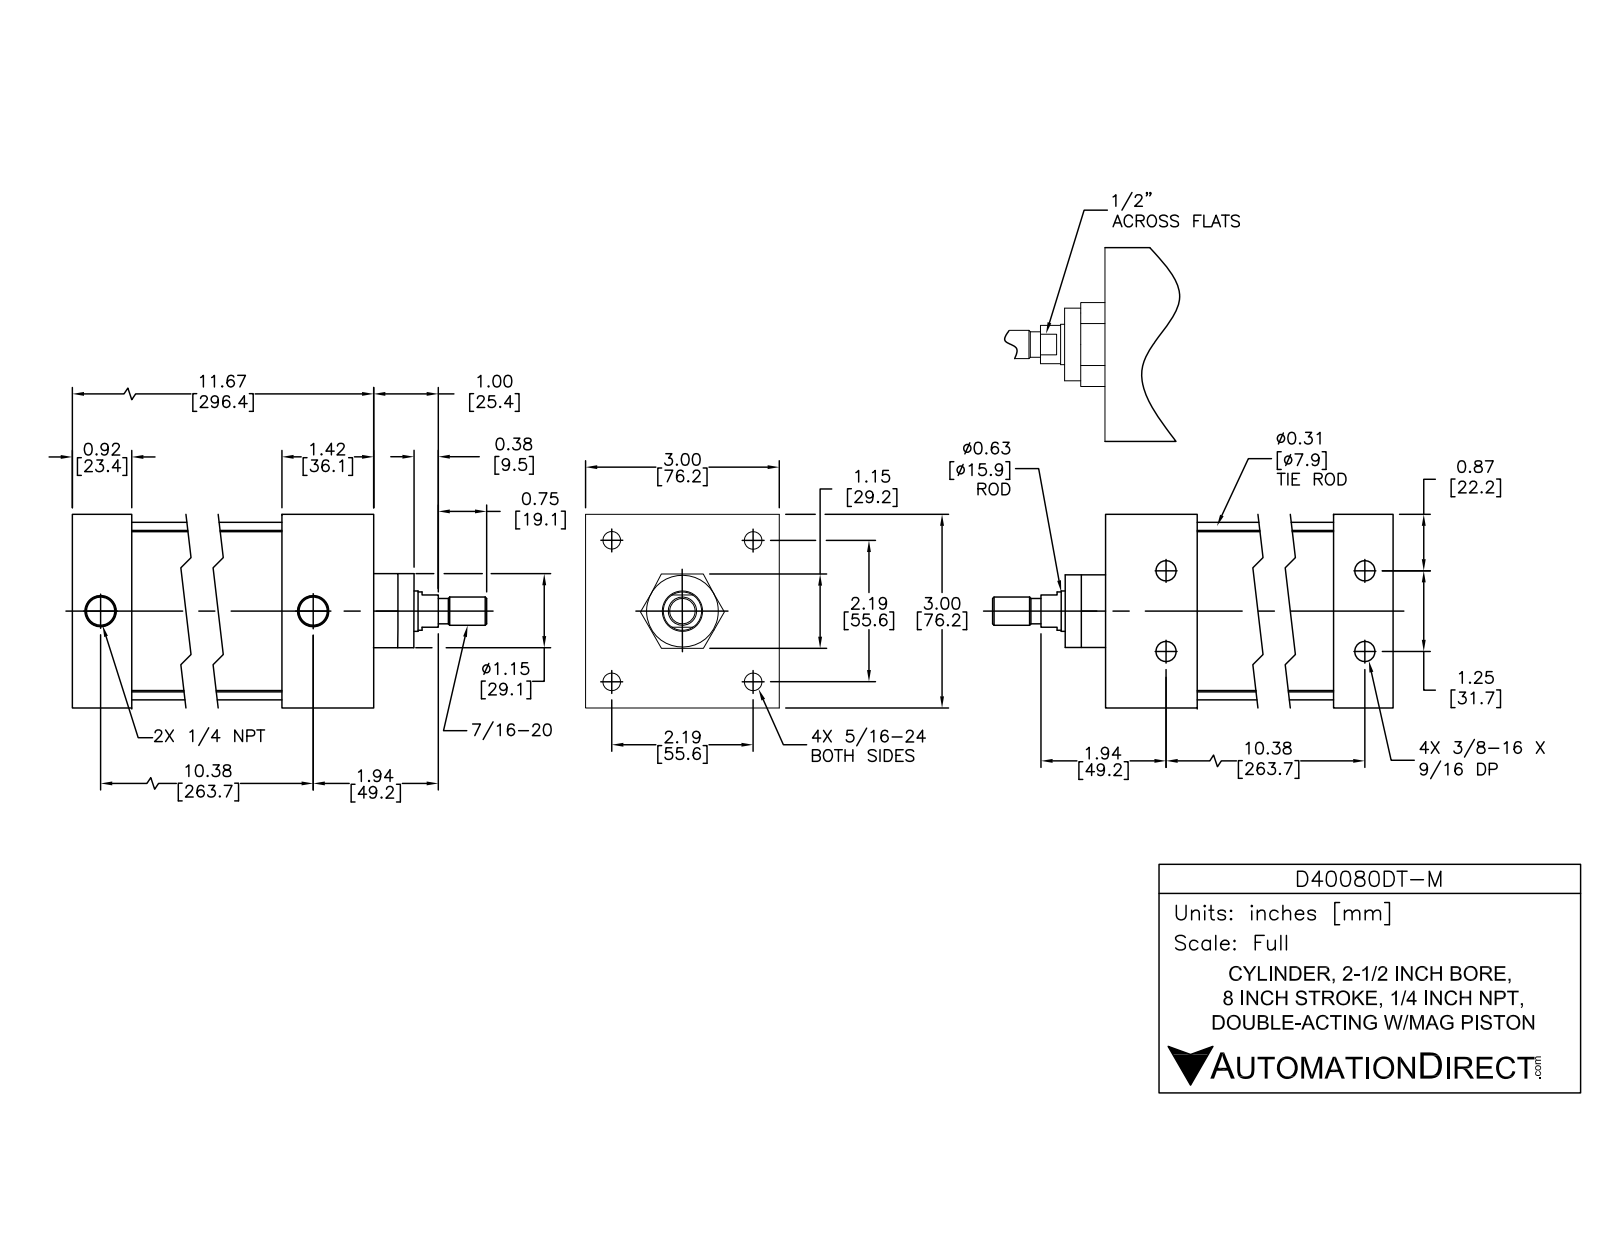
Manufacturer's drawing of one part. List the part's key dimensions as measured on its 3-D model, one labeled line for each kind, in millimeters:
Part name (STEP PRODUCT): D40080DT-M; D40080DT-M BODY; D40080DT-M PISTON
STEP written by: SolidWorks 2015 (AUTOMOTIVE_DESIGN)
Units: millimetres
Bodies: 12 solids, 298 faces (94 planar, 114 cylindrical, 90 other)
Overall size (bounding box): 342.8 × 76.2 × 76.2
Volume: 686 500 mm³ · Surface area: 212 000 mm²
Round holes (diameter × count): ⌀6.8 ×4, ⌀7.8 ×4, ⌀9.1 ×4, ⌀12.7 ×4, ⌀7.5 ×2, ⌀12.1 ×2, ⌀15.9 ×1, ⌀16 ×1, ⌀63.5 ×1
Round bosses / shafts (diameter × count): ⌀12.3 ×4, ⌀8 ×4, ⌀7.2 ×4, ⌀69.9 ×1, ⌀63.4 ×1, ⌀28.4 ×1, ⌀15.8 ×1, ⌀15 ×1
Partial cylindrical surfaces — rounded edges, fillets, slot ends (radius × count): R7.6 ×4
Main face-to-face distances: 76.2, 2, 236.9, 298.3, 272.4, 25.9, 36.1, 236.4, 262.3, 25.4
Hole centre spacings: 39.5, 55.9, 263.9, 263.4, 15.9, 15.9, 31.8, 79
